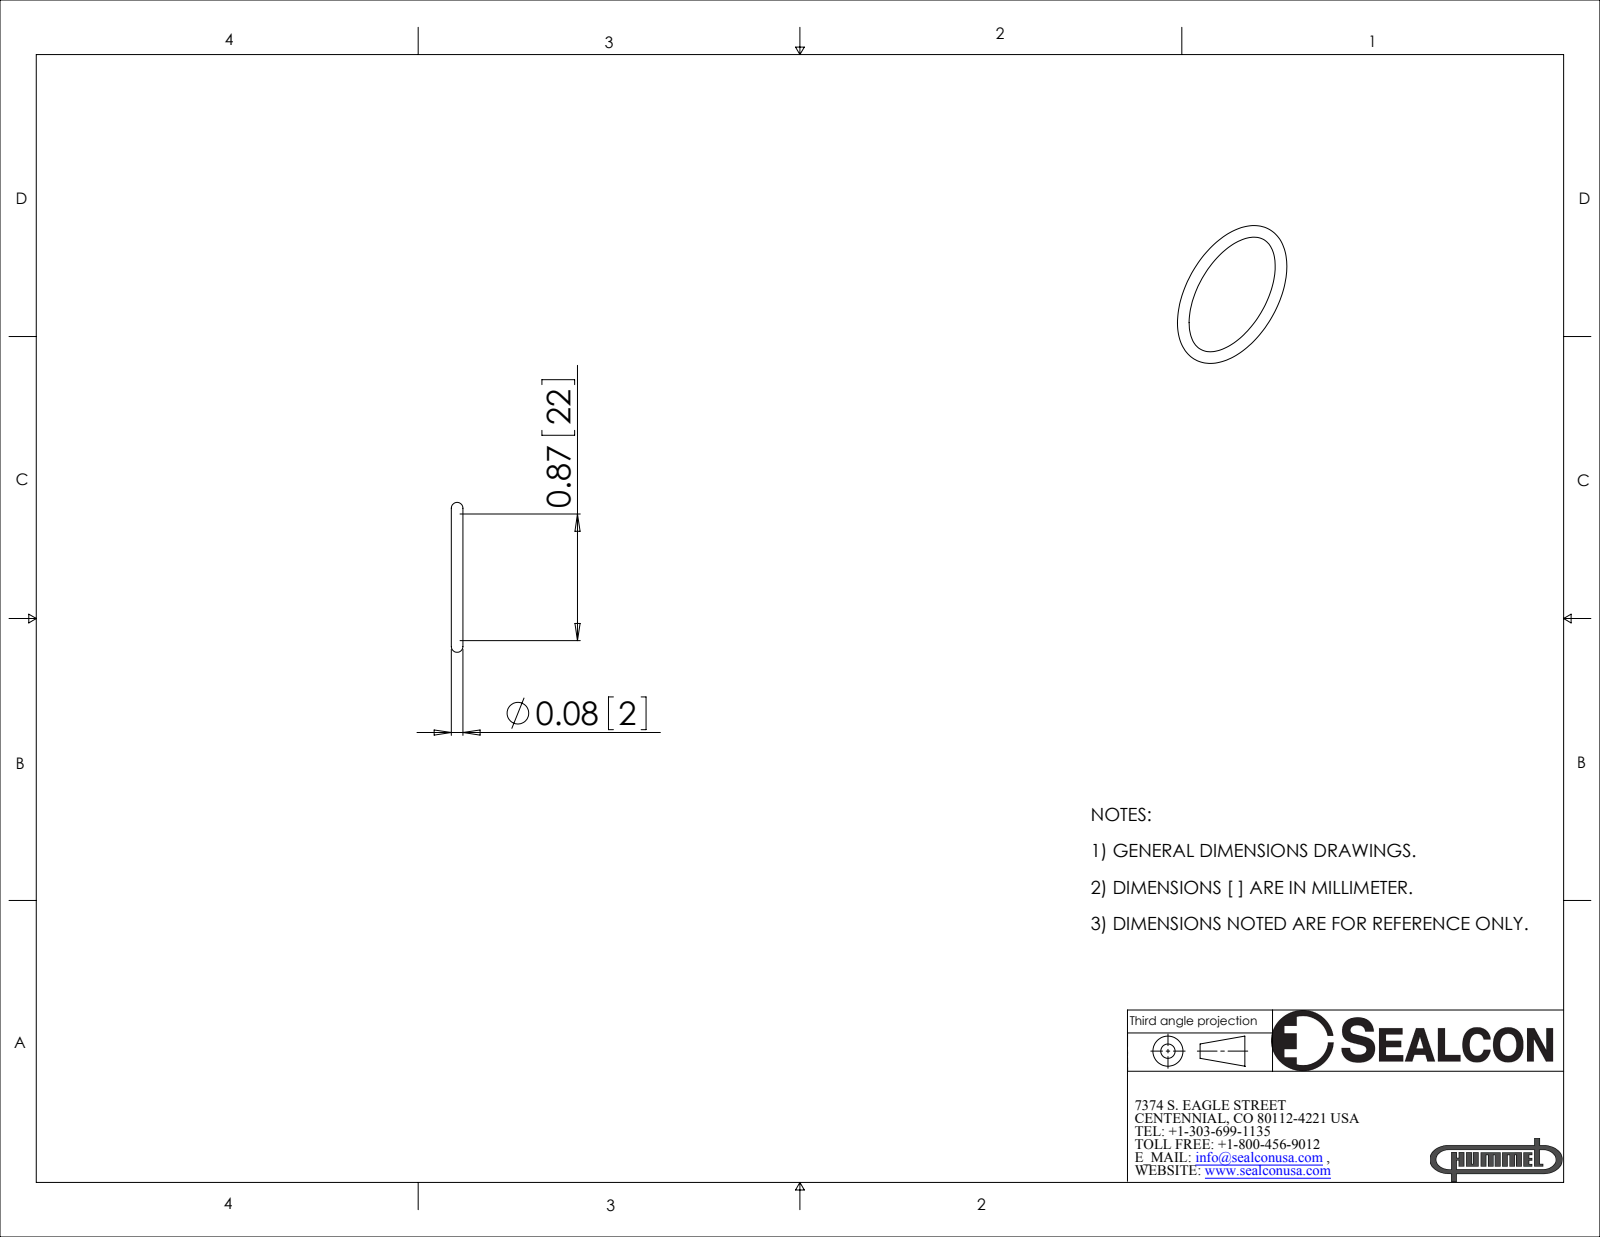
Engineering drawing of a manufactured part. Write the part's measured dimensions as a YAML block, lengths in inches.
part_name: "OR-34-SI"
step_written_by: "SolidWorks 2008 (CONFIG_CONTROL_DESIGN)"
units: inches
bodies: {solids: 1, faces: 4, planar: 0, cylindrical: 0, other: 4}
overall_size: [1.03, 1.03, 0.08]
volume: 0.015
surface_area: 0.75
